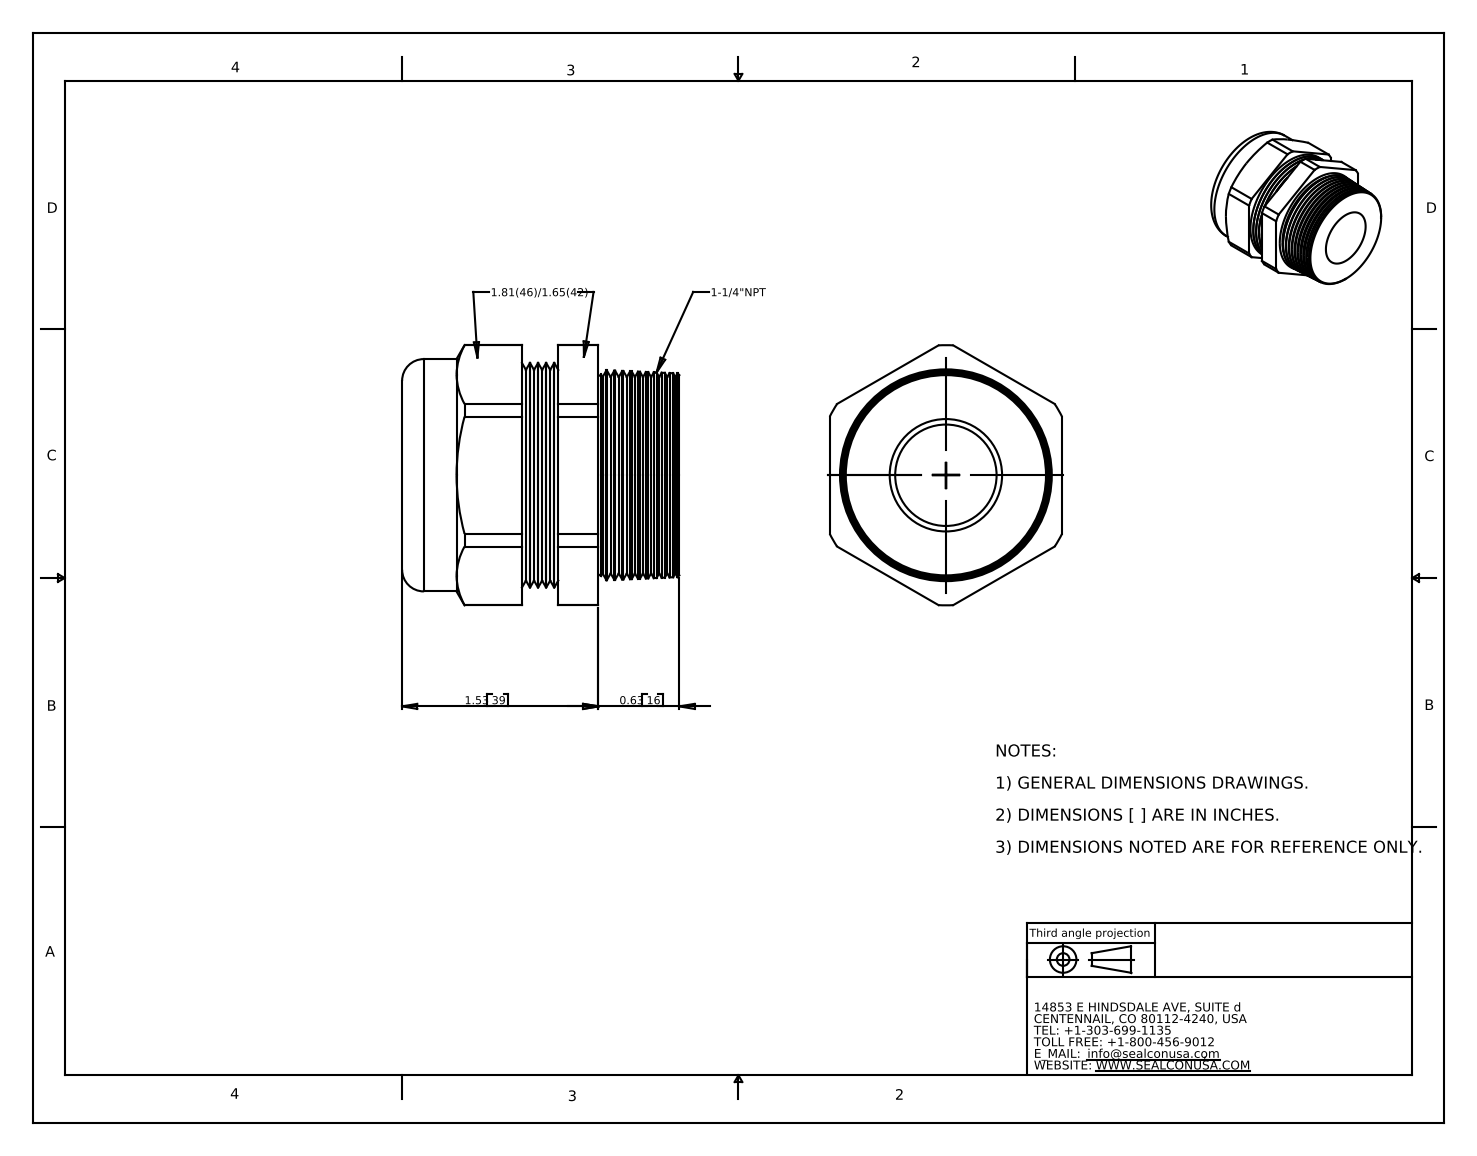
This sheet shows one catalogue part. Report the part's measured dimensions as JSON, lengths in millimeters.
{"part_name": "CD29LR-GY", "step_written_by": "SolidWorks 2007 (CONFIG_CONTROL_DESIGN)", "units": "millimeters", "bodies": {"solids": 2, "faces": 150, "planar": 20, "cylindrical": 32, "other": 98}, "overall_size": [54.9, 51.5, 46], "volume_mm3": 67090, "surface_area_mm2": 21030, "round_holes": [[20.1, 1], [35.4, 1]], "round_bosses_or_shafts": [[46, 1], [44.4, 1]], "partial_cylinders_radius": [[25.8, 1]], "face_to_face_distances": [46, 44.1, 10.3, 54.4, 38.4, 28.1, 16, 30.4, 20.1, 8]}
